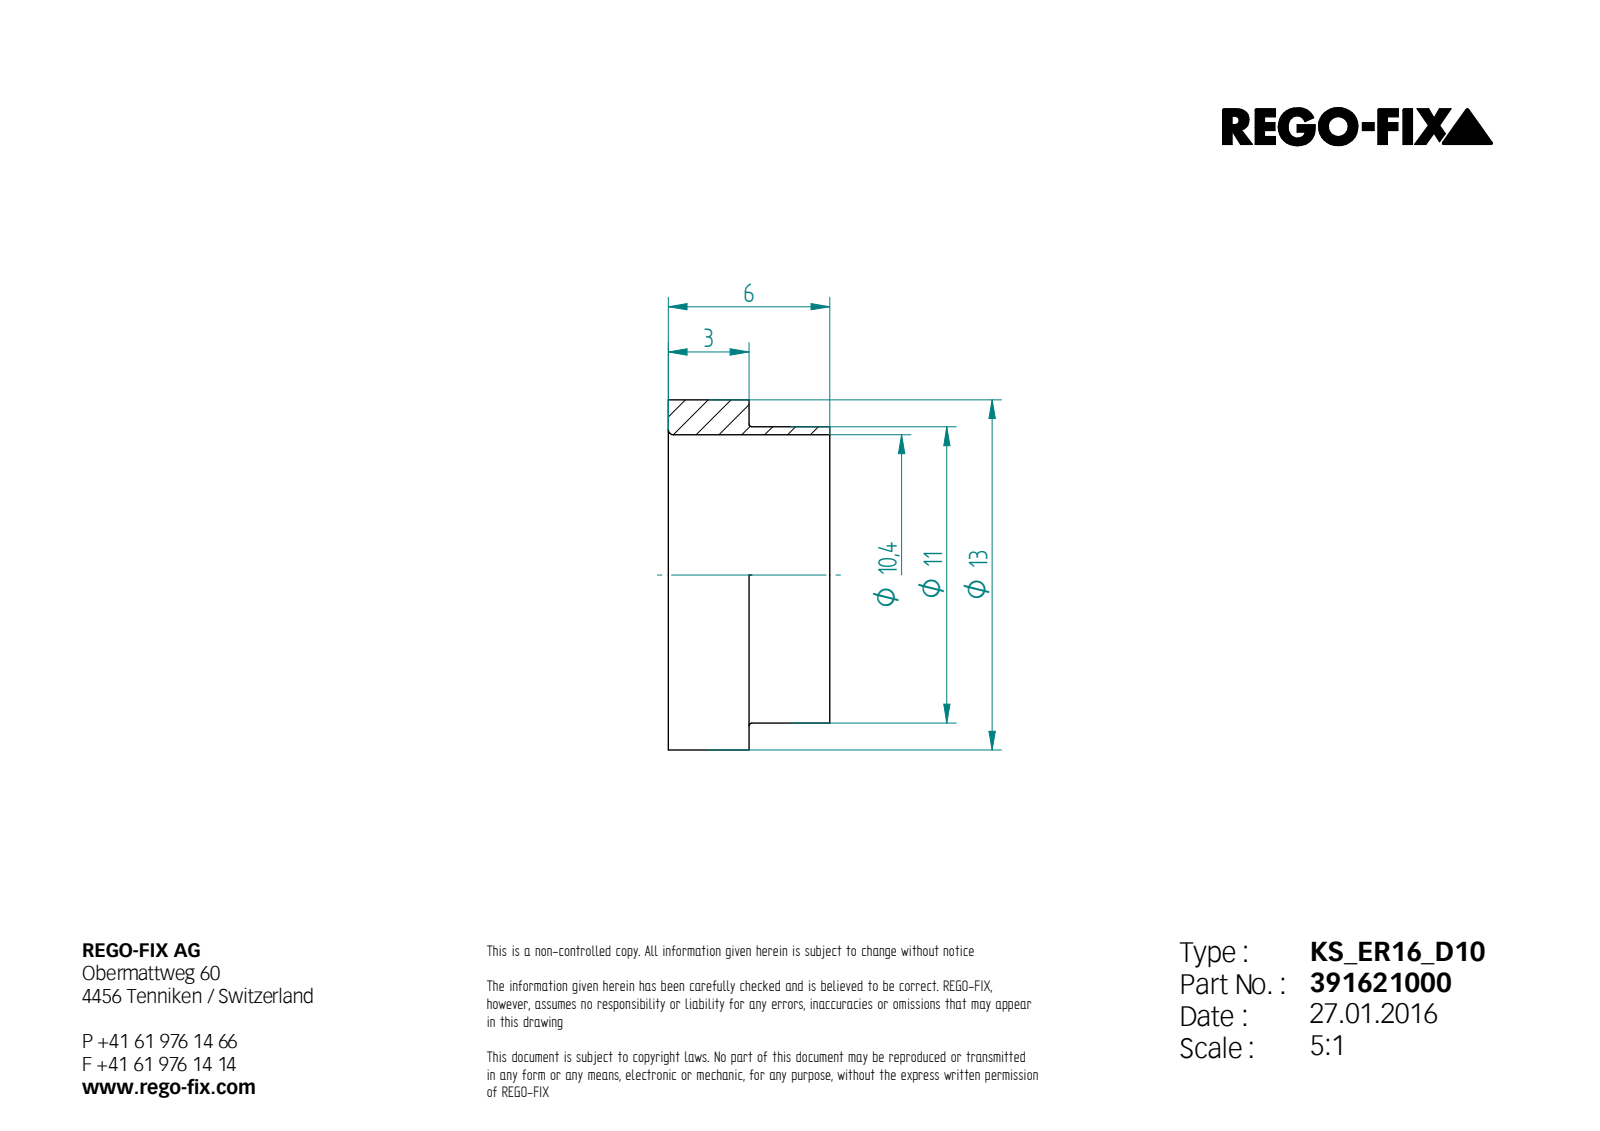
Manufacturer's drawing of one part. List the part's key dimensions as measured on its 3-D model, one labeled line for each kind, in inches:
STEP written by: Unknown (AUTOMOTIVE_DESIGN)
Units: inches
Bodies: 1 solid, 8 faces (3 planar, 3 cylindrical, 2 other)
Overall size (bounding box): 0.512 × 0.512 × 0.236
Volume: 0.011 in³ · Surface area: 0.797 in²
Round holes (diameter × count): ⌀0.409 ×1
Round bosses / shafts (diameter × count): ⌀0.512 ×1, ⌀0.433 ×1
Main face-to-face distances: 0.118, 0.236
